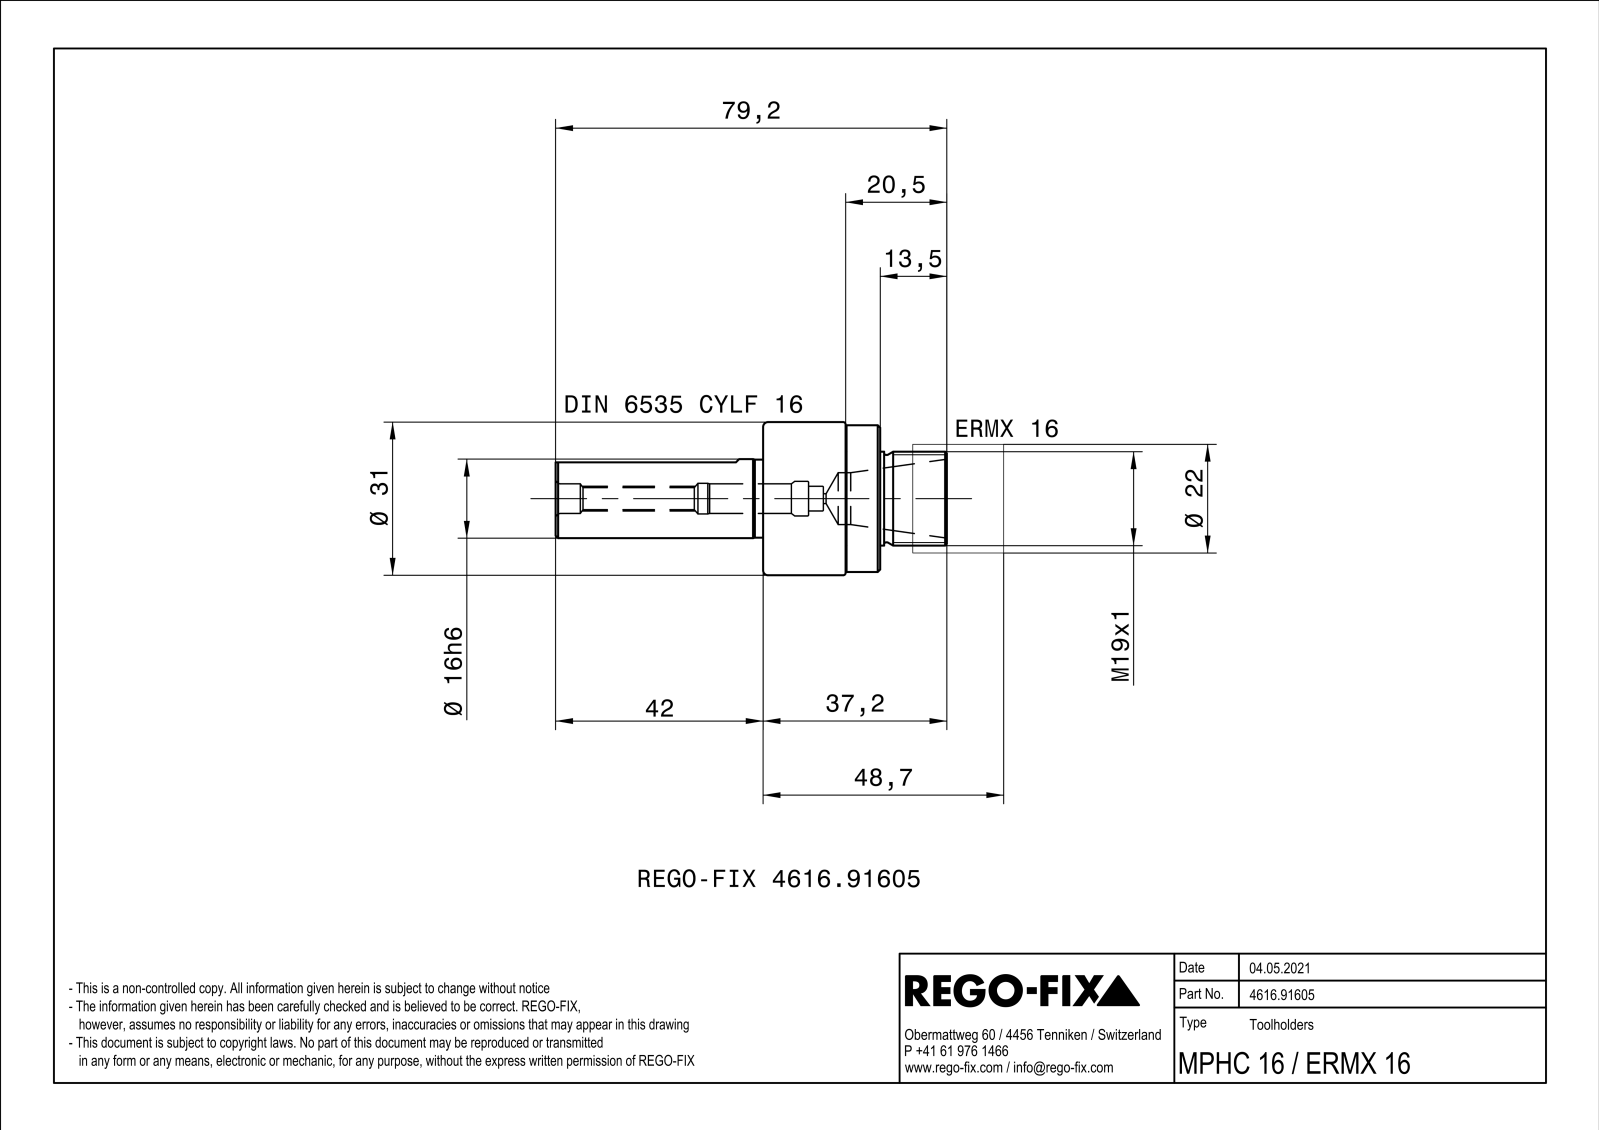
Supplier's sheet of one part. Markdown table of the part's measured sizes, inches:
| quantity | value |
| --- | --- |
| part name | NOCUT |
| STEP written by | SIEMENS PLM Software Solid Edge ST10 (AUTOMOTIVE_DESIGN) |
| units | inches |
| bodies | 6 solids, 110 faces (27 planar, 35 cylindrical, 48 other) |
| overall size | 3.118 × 1.22 × 1.22 |
| volume | 1.359 in³ |
| surface area | 25.18 in² |
| round holes (diameter × count) | 0.098 × 4, 0.098 × 2, 0.062 × 1, 0.079 × 1, 0.176 × 1, 0.197 × 1, 0.236 × 1, 0.244 × 1, 0.276 × 1, 0.413 × 1, 0.787 × 1, 1.063 × 1 |
| round bosses / shafts (diameter × count) | 1.22 × 1, 1.169 × 1, 1.102 × 1, 1.024 × 1, 0.748 × 1, 0.736 × 1, 0.697 × 1, 0.63 × 1 |
| main face-to-face distances | 0.657, 0.236, 0.894, 0.079, 0.531, 0.421, 0.571, 0.295, 0.126, 0.362 |
| hole center spacings | 0.453, 0.64, 0.906 |
